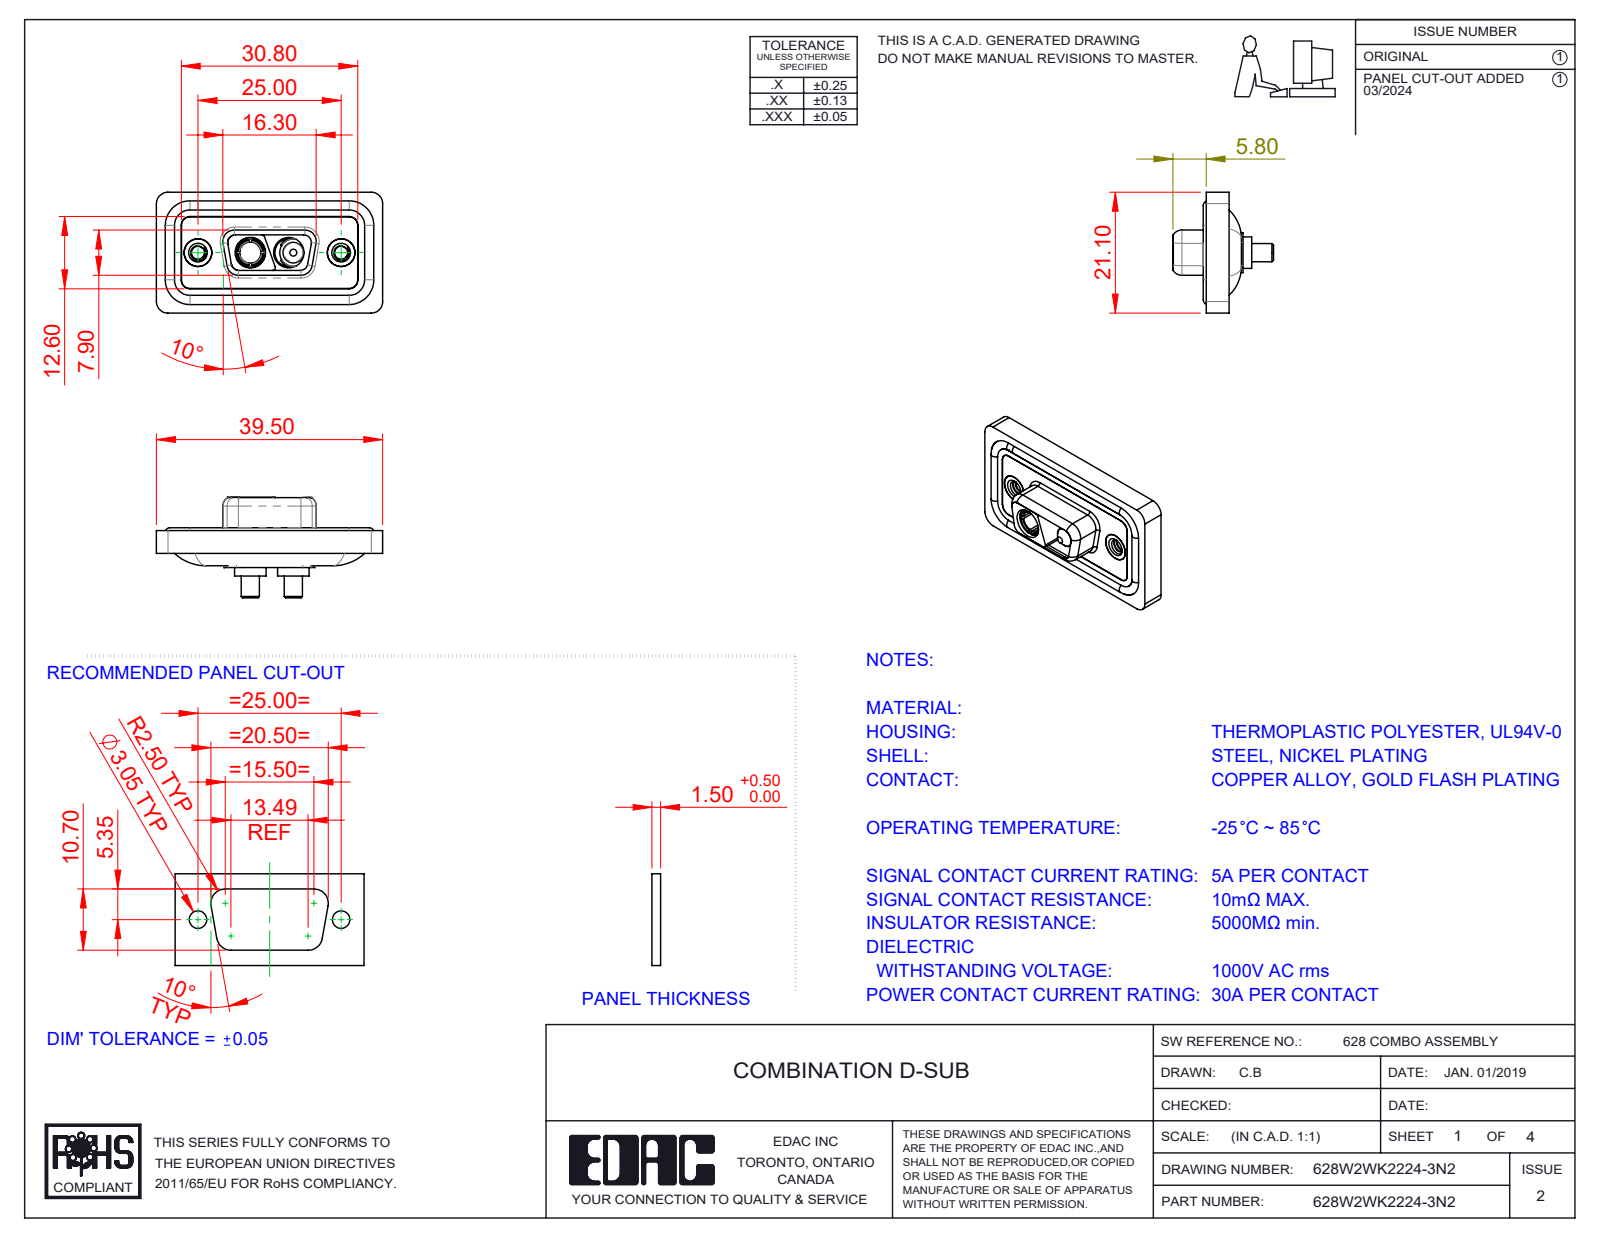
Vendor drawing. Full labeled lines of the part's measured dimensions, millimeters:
Part name (STEP PRODUCT): Power Pin_30A S; 628Combo Shell Rear_09 Contacts; 628Combo Threaded Rivet_2; Power Socket_30A S (+4 more)
STEP written by: SolidWorks 2023 (CONFIG_CONTROL_DESIGN)
Units: millimetres
Bodies: 11 solids, 500 faces (144 planar, 231 cylindrical, 125 other)
Overall size (bounding box): 39.5 × 21.1 × 17.55
Volume: 4 617 mm³ · Surface area: 7 353 mm²
Round holes (diameter × count): ⌀4.85 ×4, ⌀2.26 ×2, ⌀4 ×2, ⌀4.05 ×2, ⌀5 ×2, ⌀5.3 ×2, ⌀3.7 ×1
Round bosses / shafts (diameter × count): ⌀1.6 ×4, ⌀5.5 ×2, ⌀5.2 ×2, ⌀4.95 ×2, ⌀4.8 ×2, ⌀4.75 ×2, ⌀3.75 ×2, ⌀3.2 ×2
Partial cylindrical surfaces — rounded edges, fillets, slot ends (radius × count): R1.5 ×22, R2 ×18, R1.35 ×8, R1.6 ×8, R0.5 ×6, R0.25 ×4, R0.6 ×4, R0.65 ×4
Main face-to-face distances: 0.4, 1.1, 2.9, 1.6, 0.5, 1.8, 5.65, 1.5, 5.35, 3.1
Hole centre spacings: 9.14, 15.86, 6.72, 25
